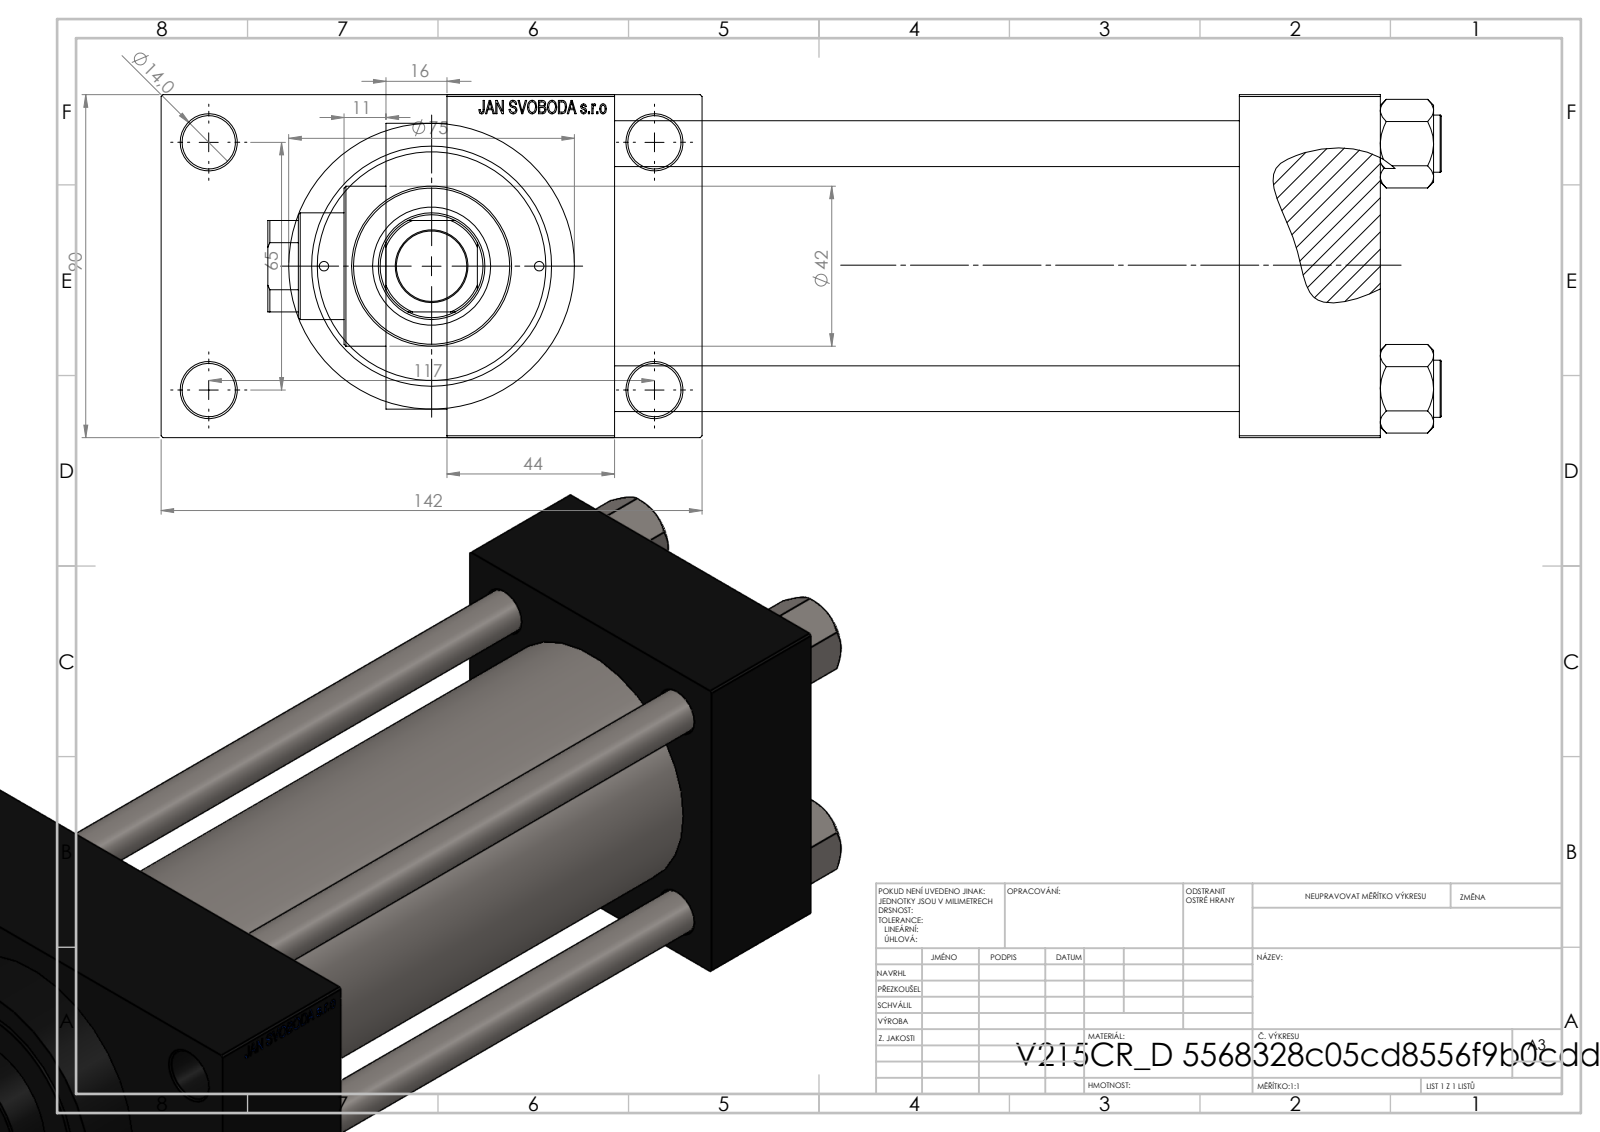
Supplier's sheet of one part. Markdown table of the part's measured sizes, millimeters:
| quantity | value |
| --- | --- |
| part name | V215CR_D_TYCINKA; V215CR_VCP_D; V215CR_D_Body; V215_VC_A (+1 more) |
| STEP written by | SolidWorks 2019 (CONFIG_CONTROL_DESIGN) |
| units | millimeters |
| bodies | 11 solids, 1111 faces (499 planar, 92 cylindrical, 520 other) |
| overall size | 308 × 142 × 90 |
| volume | 1 274 000 mm³ |
| surface area | 268 842 mm² |
| round holes (diameter × count) | 12 × 4, 14 × 4, 2.5 × 2, 7 × 2, 20.96 × 2, 30 × 2, 18.5 × 1, 28 × 1, 31 × 1, 50 × 1, 60 × 1, 63 × 1 |
| round bosses / shafts (diameter × count) | 15 × 4, 75 × 1, 69 × 1, 42 × 1 |
| partial cylindrical surfaces (radius × count) | 13.5 × 1 |
| main face-to-face distances | 90, 164, 37, 201, 208, 245, 44, 26, 116, 16 |
| hole center spacings | 26.35, 32.39, 44.4, 45.47, 64.3, 66.92, 68.42, 69.81 |
